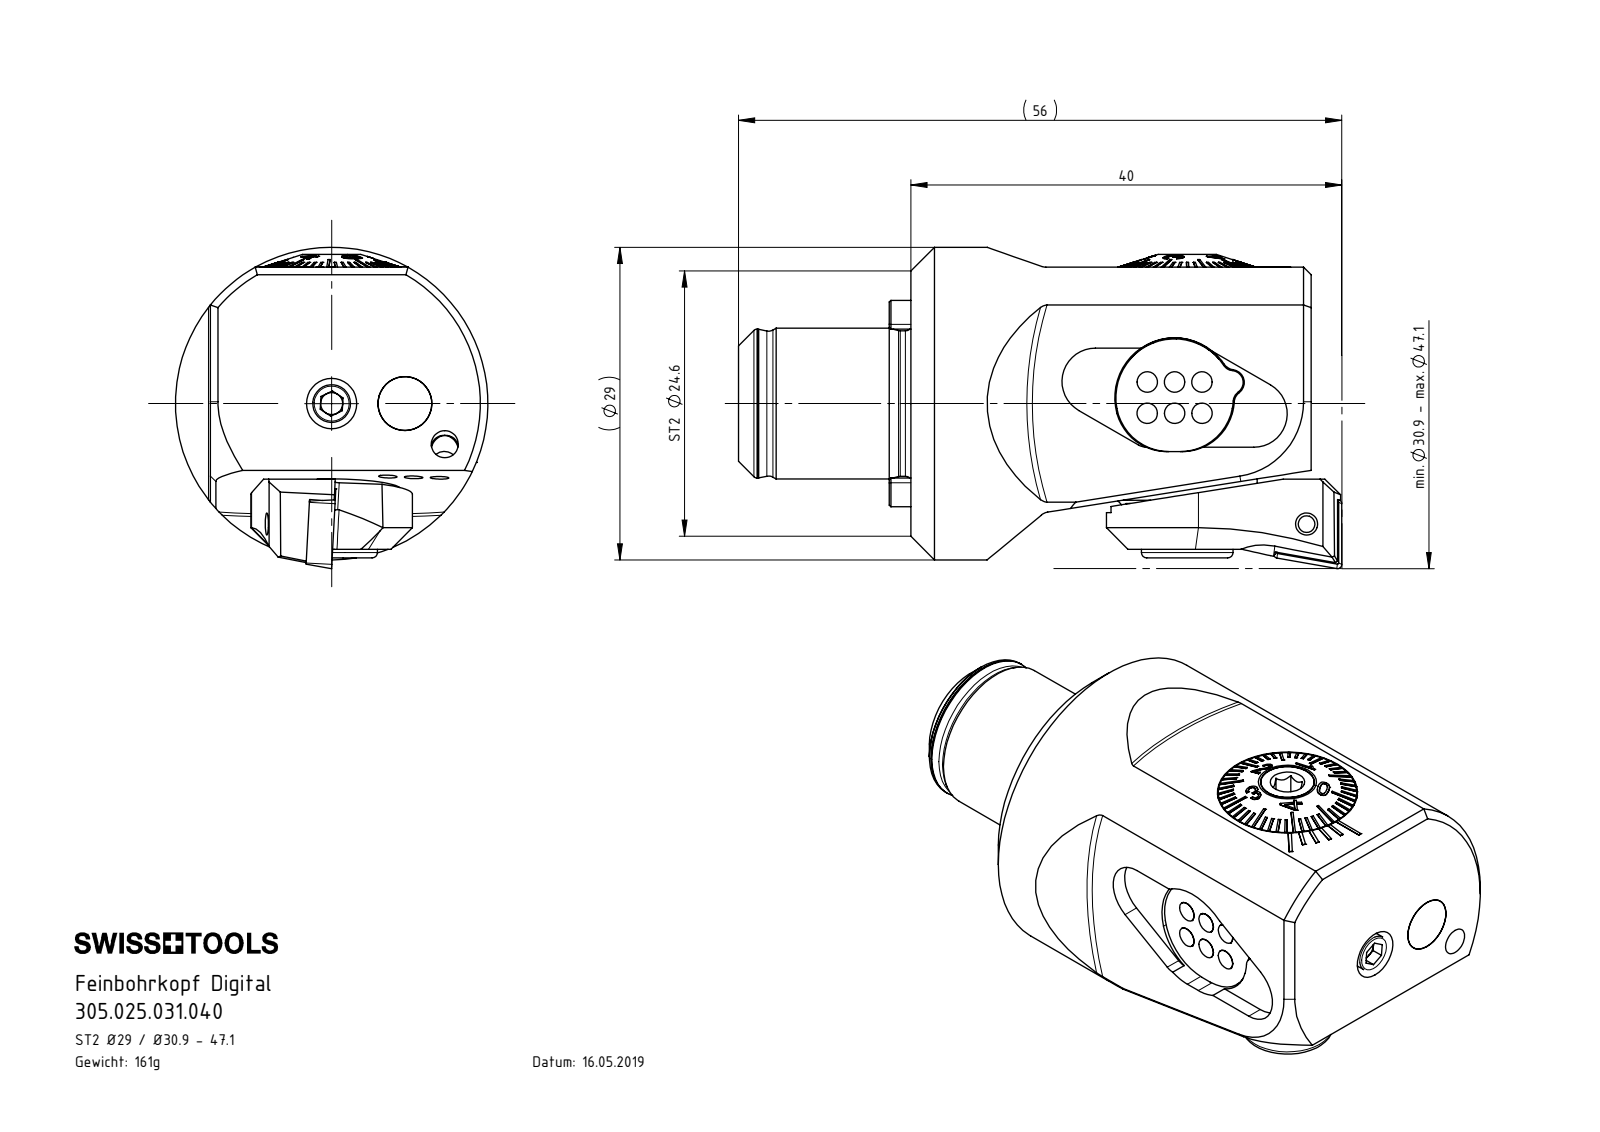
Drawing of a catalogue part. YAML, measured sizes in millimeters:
part_name: "ISO 4026 - M5 x 4_PreviewCfg; Fxx-MAB.xxx.xxx_A_F25x1x2; F25-BG1.DA2.013_Aktuell 0.6.2014-M1x2; F25-WCA.001.006 (+8 more)"
step_written_by: "SolidWorks 2015 (AUTOMOTIVE_DESIGN)"
units: millimeters
bodies: {solids: 22, faces: 949, planar: 399, cylindrical: 211, other: 339}
overall_size: [56, 27.7, 25]
volume: 18312
surface_area: 11738
round_holes:
  - {diameter: 2, count: 4}
  - {diameter: 2.05, count: 3}
  - {diameter: 2.2, count: 2}
  - {diameter: 4.2, count: 2}
  - {diameter: 5, count: 2}
  - {diameter: 0.7, count: 1}
  - {diameter: 2.1, count: 1}
  - {diameter: 2.4, count: 1}
  - {diameter: 2.7, count: 1}
  - {diameter: 2.8, count: 1}
  - {diameter: 3, count: 1}
  - {diameter: 3.3, count: 1}
round_bosses_or_shafts:
  - {diameter: 1.9, count: 6}
  - {diameter: 2.2, count: 3}
  - {diameter: 5, count: 2}
  - {diameter: 4.95, count: 2}
  - {diameter: 2.5, count: 2}
  - {diameter: 25, count: 1}
  - {diameter: 14, count: 1}
  - {diameter: 13.8, count: 1}
partial_cylinders:
  - {radius: 0.5, count: 8}
  - {radius: 0.21, count: 6}
  - {radius: 0.36, count: 5}
  - {radius: 1.1, count: 3}
  - {radius: 1.2, count: 3}
  - {radius: 1.32, count: 2}
  - {radius: 1.4, count: 2}
  - {radius: 1.98, count: 2}
face_to_face_distances: [37.15, 1.5, 4.25, 19.95, 0.8, 3.1, 3.9, 19.6, 15.7, 18.8]
hole_center_spacings: [2.6, 8.38, 10.79, 0.68, 3.84, 3.99, 4.48, 6.8]
